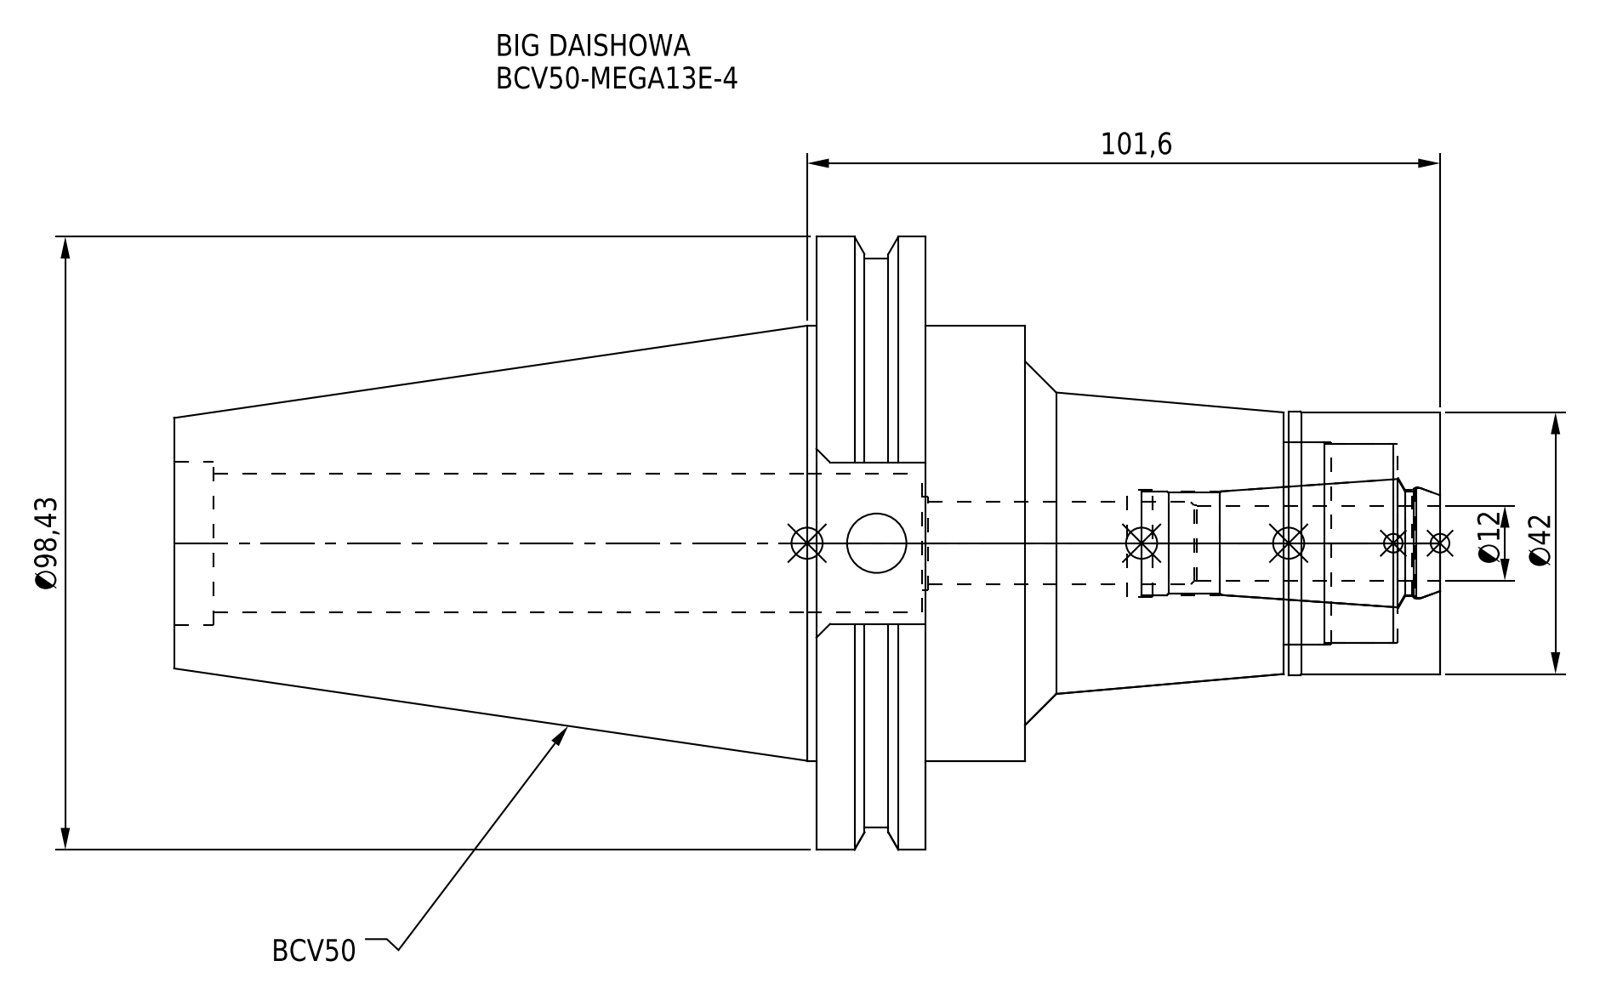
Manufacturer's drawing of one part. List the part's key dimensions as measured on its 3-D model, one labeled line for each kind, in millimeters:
Part name (STEP PRODUCT): MEN13_1.stp; DXF_TEMP_ASSY_ASM_4_ASM.stp; BCV50-MEGA13E-4; BCV50-MEGA13E-4-120-FreeParts (+3 more)
STEP written by: SolidWorks 2019 (CONFIG_CONTROL_DESIGN)
Units: millimetres
Bodies: 2 solids, 93 faces (31 planar, 42 cylindrical, 20 other)
Overall size (bounding box): 203.2 × 98.42 × 94.95
Volume: 471 009 mm³ · Surface area: 66 592 mm²
Round holes (diameter × count): ⌀9.53 ×1, ⌀13.3 ×1, ⌀15 ×1, ⌀16.6 ×1, ⌀17 ×1, ⌀17.2 ×1, ⌀17.9 ×1, ⌀22.3 ×1, ⌀26.23 ×1, ⌀32 ×1, ⌀32.5 ×1
Round bosses / shafts (diameter × count): ⌀98.42 ×1, ⌀91.29 ×1, ⌀69.85 ×1, ⌀42.3 ×1, ⌀42 ×1
Main face-to-face distances: 17.55, 82.55, 100.1, 66.6, 15.95, 33.5, 203.2, 136.6, 120.65, 103.1
